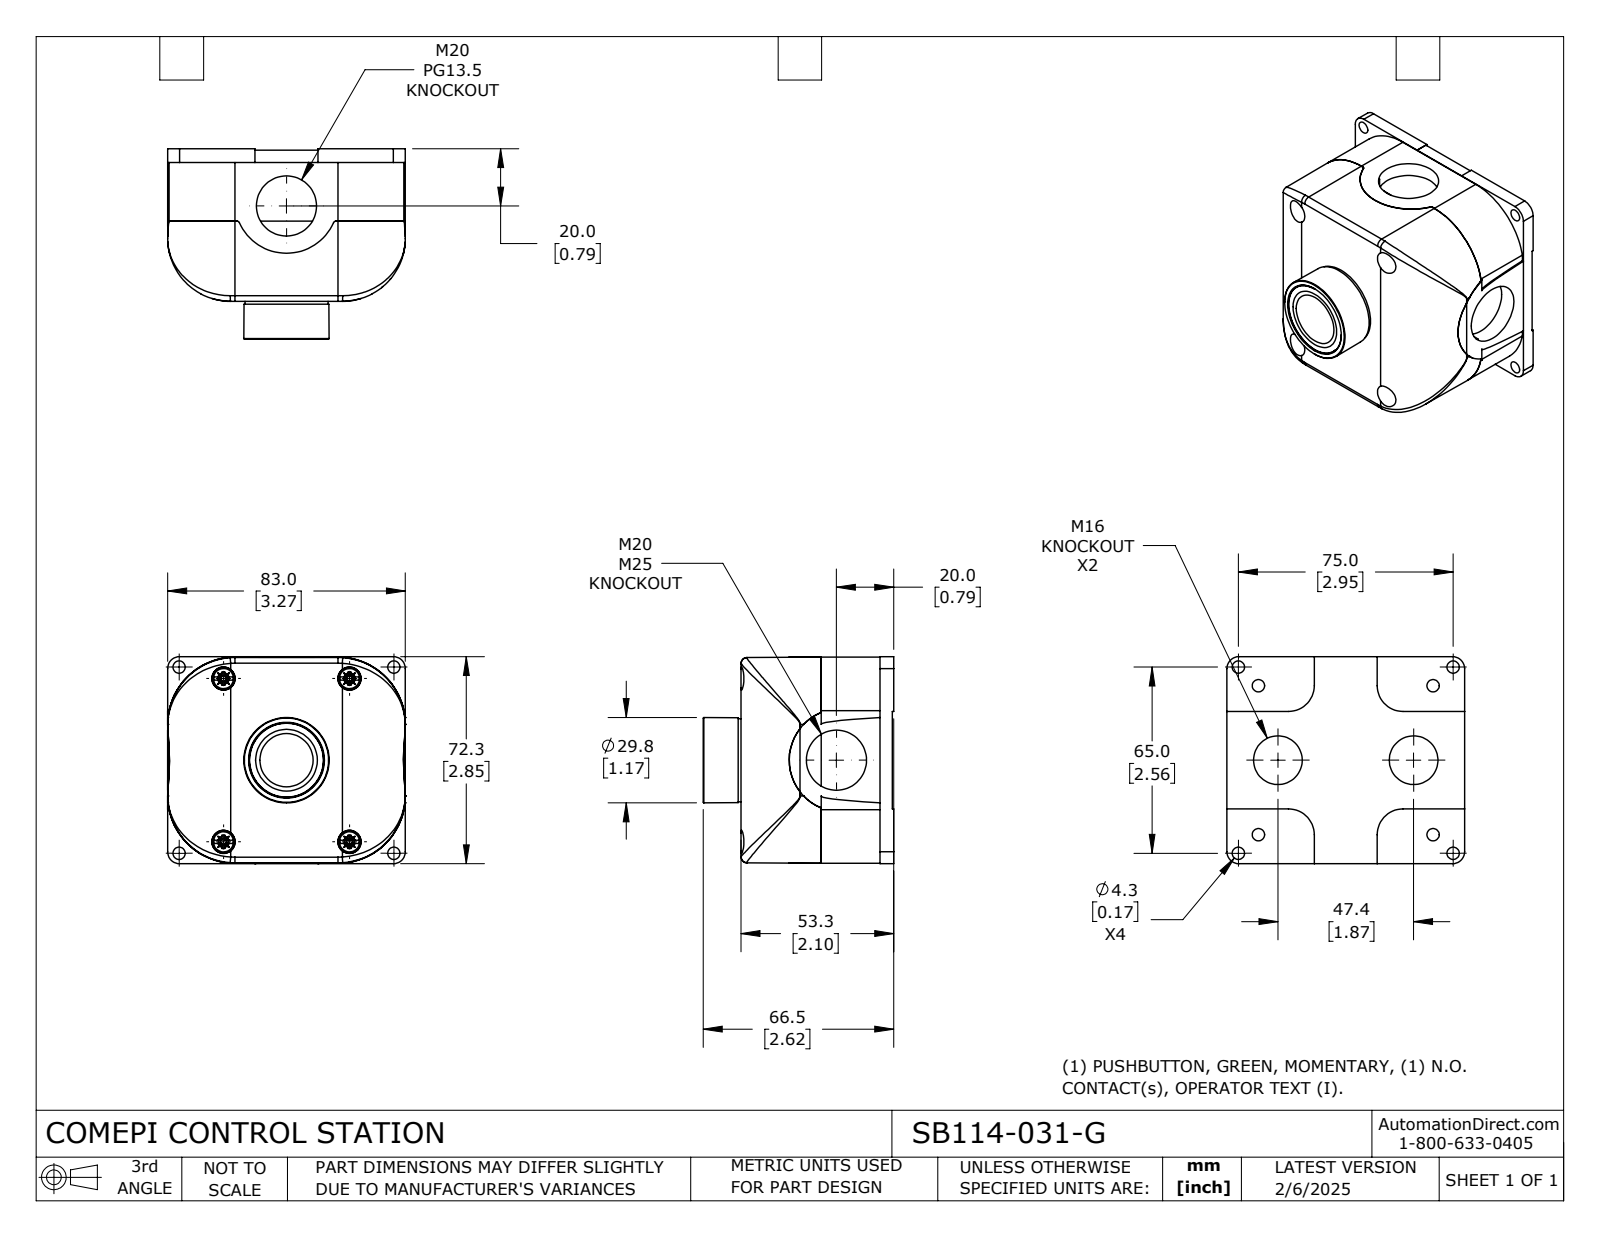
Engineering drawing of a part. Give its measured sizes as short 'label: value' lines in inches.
name: SB114-031-G
written by: SolidWorks 2024 (CONFIG_CONTROL_DESIGN)
unit: in
bodies: 4 solids, 548 faces (300 planar, 144 cylindrical, 104 other)
size: 3.268 × 2.846 × 2.618
volume: 12.8 in³; area: 89.33 in²
holes: 8× ⌀0.169, 4× ⌀0.323, 2× ⌀0.669, 2× ⌀0.827, 1× ⌀0.531, 1× ⌀0.713, 1× ⌀0.854
bosses: 4× ⌀0.276, 1× ⌀1.142, 1× ⌀1.016, 1× ⌀0.748, 1× ⌀0.728, 1× ⌀0.63, 1× ⌀0.614, 1× ⌀0.61
rounds: 4× R0.035, 4× R0.079, 4× R0.354, 4× R0.38, 4× R0.925, 2× R0.008, 2× R0.01, 2× R0.709
face distances: 0.976, 0.098, 0.878, 2.079, 1.98, 1.102, 0.118, 2.098, 0.02, 0.996
hole spacings: 0.376, 1.058, 1.39, 1.578, 1.954, 2.32, 2.367, 2.689
